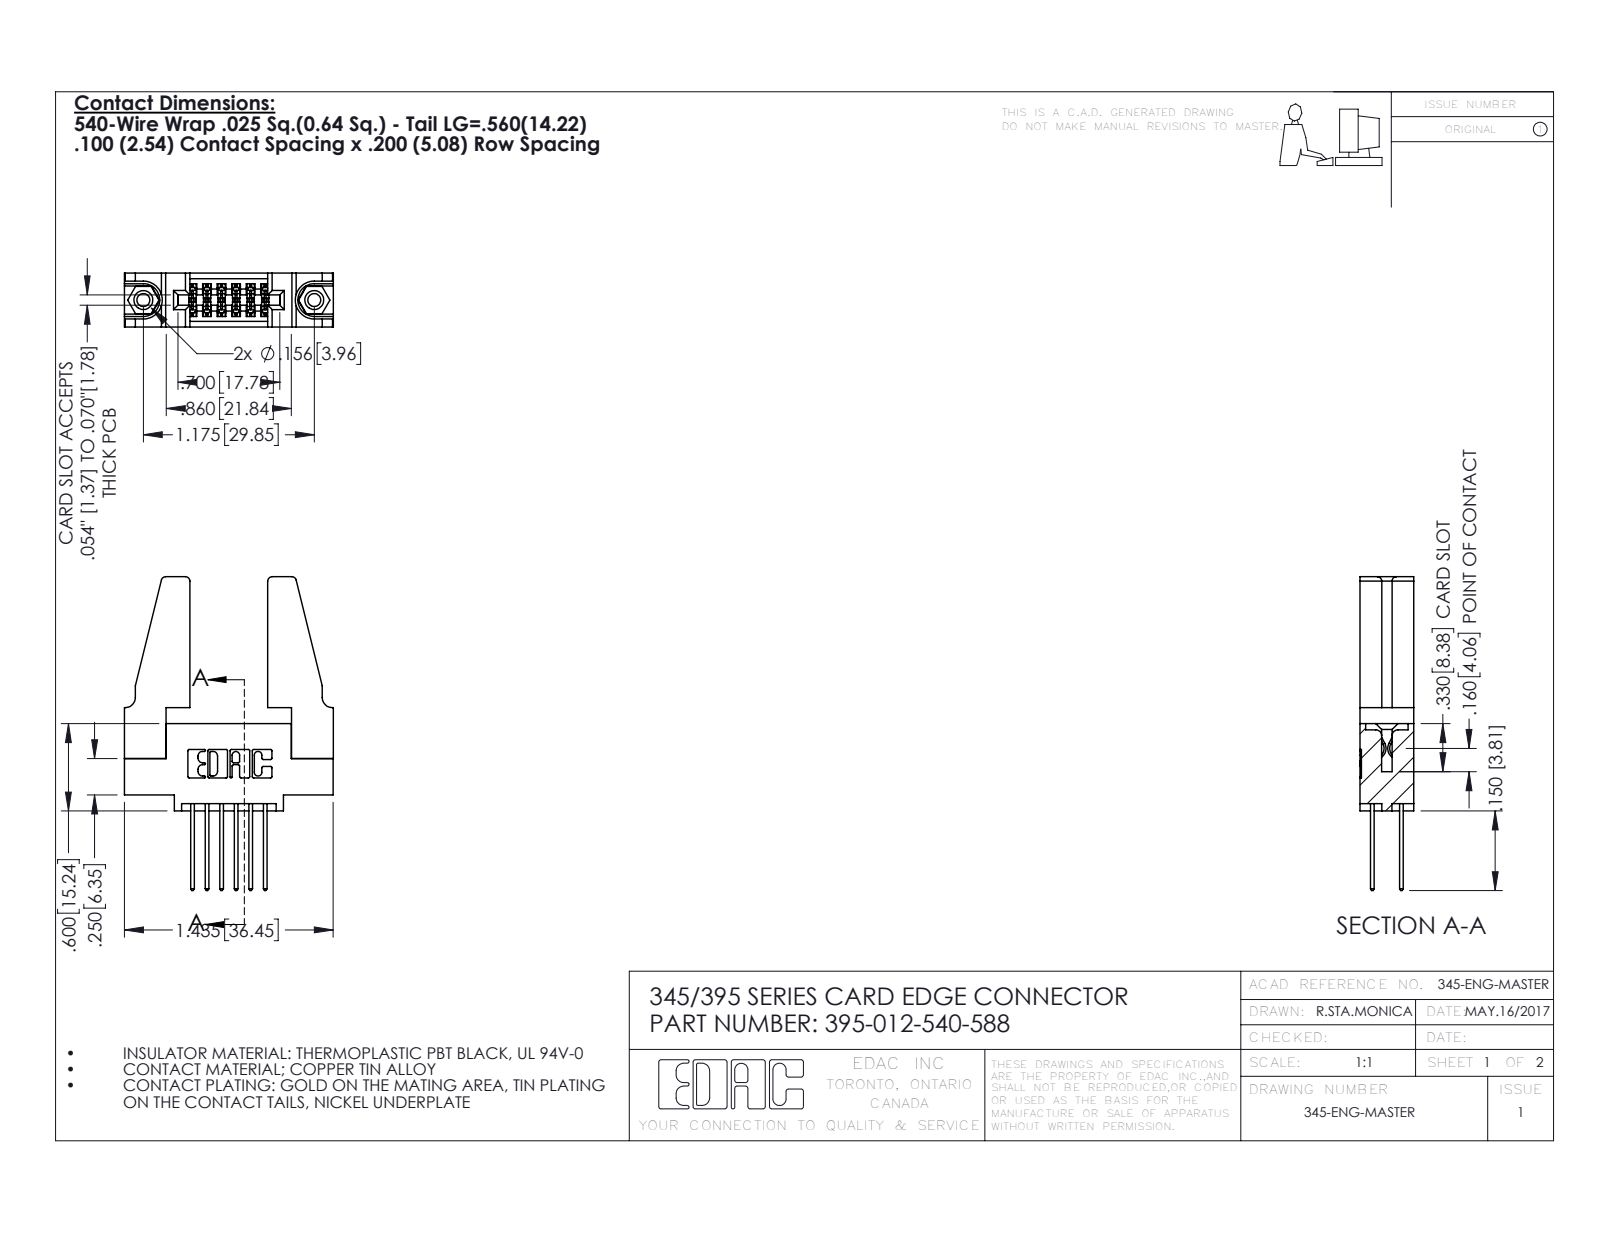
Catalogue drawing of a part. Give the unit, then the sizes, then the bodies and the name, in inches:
Units: inches
Overall size (bounding box): 2.157 × 1.436 × 0.37
Round holes (diameter × count): ⌀0.089 ×2, ⌀0.125 ×2, ⌀0.156 ×2, ⌀0.064 ×1
Round bosses / shafts (diameter × count): ⌀0.155 ×2
Partial cylindrical surfaces — rounded edges, fillets, slot ends (radius × count): R0.01 ×22, R0.006 ×18, R0.01 ×12, R0.03 ×8, R0.007 ×6, R0.031 ×6, R0.026 ×3, R0.014 ×2
Main face-to-face distances: 0.37, 0.072, 0.298, 0.2, 0.098, 0.272, 0.025, 0.225, 0.15, 0.148
Hole centre spacings: 0.27, 0.946, 1.175
Volume: 0.393 in³ · Surface area: 11.52 in²
Bodies: 17 solids, 854 faces (552 planar, 286 cylindrical, 16 other)
Part name (STEP PRODUCT): 395-012-540-588; 345-292-001_345-293-140; 345 Part_0.110 Offset - 0.156 Dia-TH; 345-220-078_345-220-088 (+1 more)
STEP written by: SolidWorks 2016 (CONFIG_CONTROL_DESIGN)
